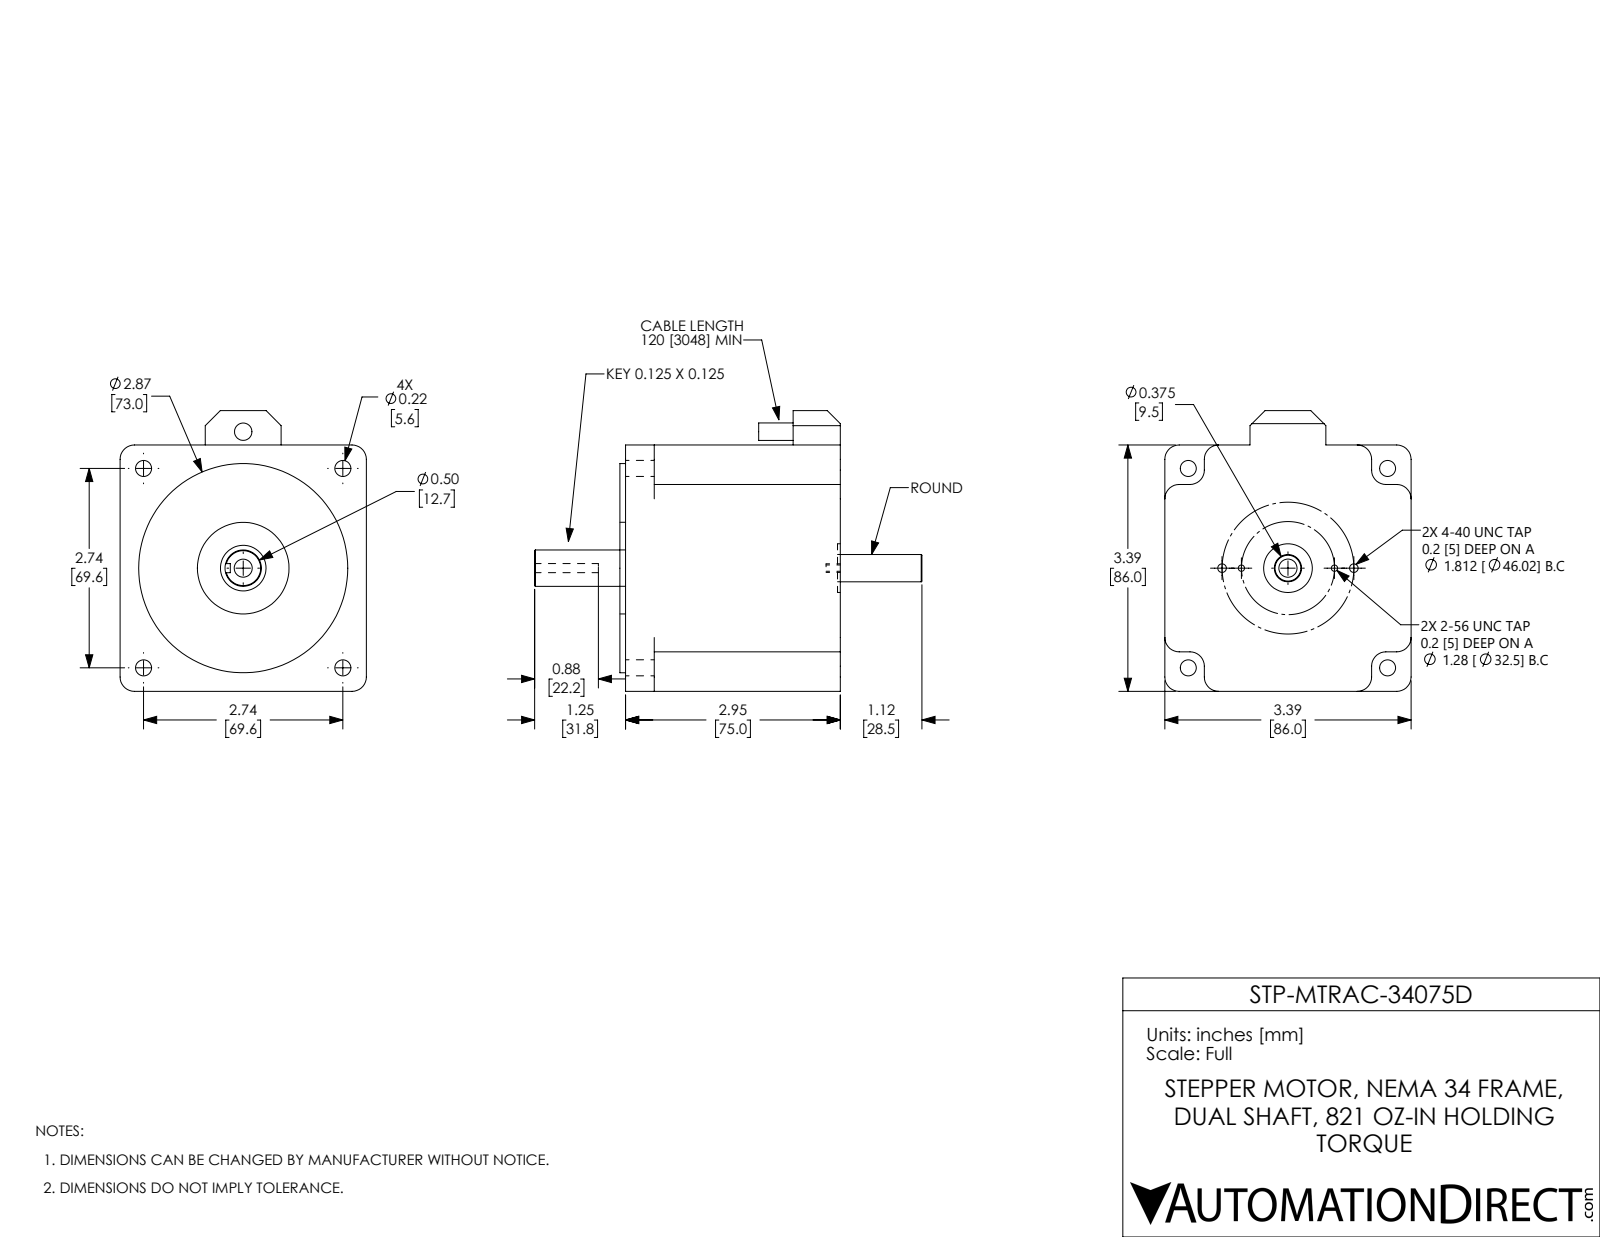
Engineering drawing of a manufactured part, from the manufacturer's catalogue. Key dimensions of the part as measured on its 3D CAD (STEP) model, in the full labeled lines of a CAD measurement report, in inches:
Part name (STEP PRODUCT): STP-MTRAC-34075D from HT34-695 75mm from 696_117mm r1
STEP written by: SolidWorks 2017 (AUTOMOTIVE_DESIGN)
Units: inches
Bodies: 1 solid, 88 faces (39 planar, 44 cylindrical, 5 other)
Overall size (bounding box): 5.325 × 3.858 × 3.386
Volume: 31.73 in³ · Surface area: 67.31 in²
Round holes (diameter × count): ⌀0.22 ×4, ⌀0.087 ×2, ⌀0.118 ×2, ⌀0.669 ×1, ⌀1.26 ×1
Round bosses / shafts (diameter × count): ⌀2.875 ×1, ⌀0.5 ×1, ⌀0.375 ×1, ⌀0.24 ×1
Partial cylindrical surfaces — rounded edges, fillets, slot ends (radius × count): R0.197 ×16
Main face-to-face distances: 3.386, 2.953, 3.031, 0.079, 0.543, 2.843, 2.3, 0.472, 2.559, 0.394
Hole centre spacings: 1.446, 1.553, 1.937, 2.432, 2.657, 2.74, 0.266, 0.64
